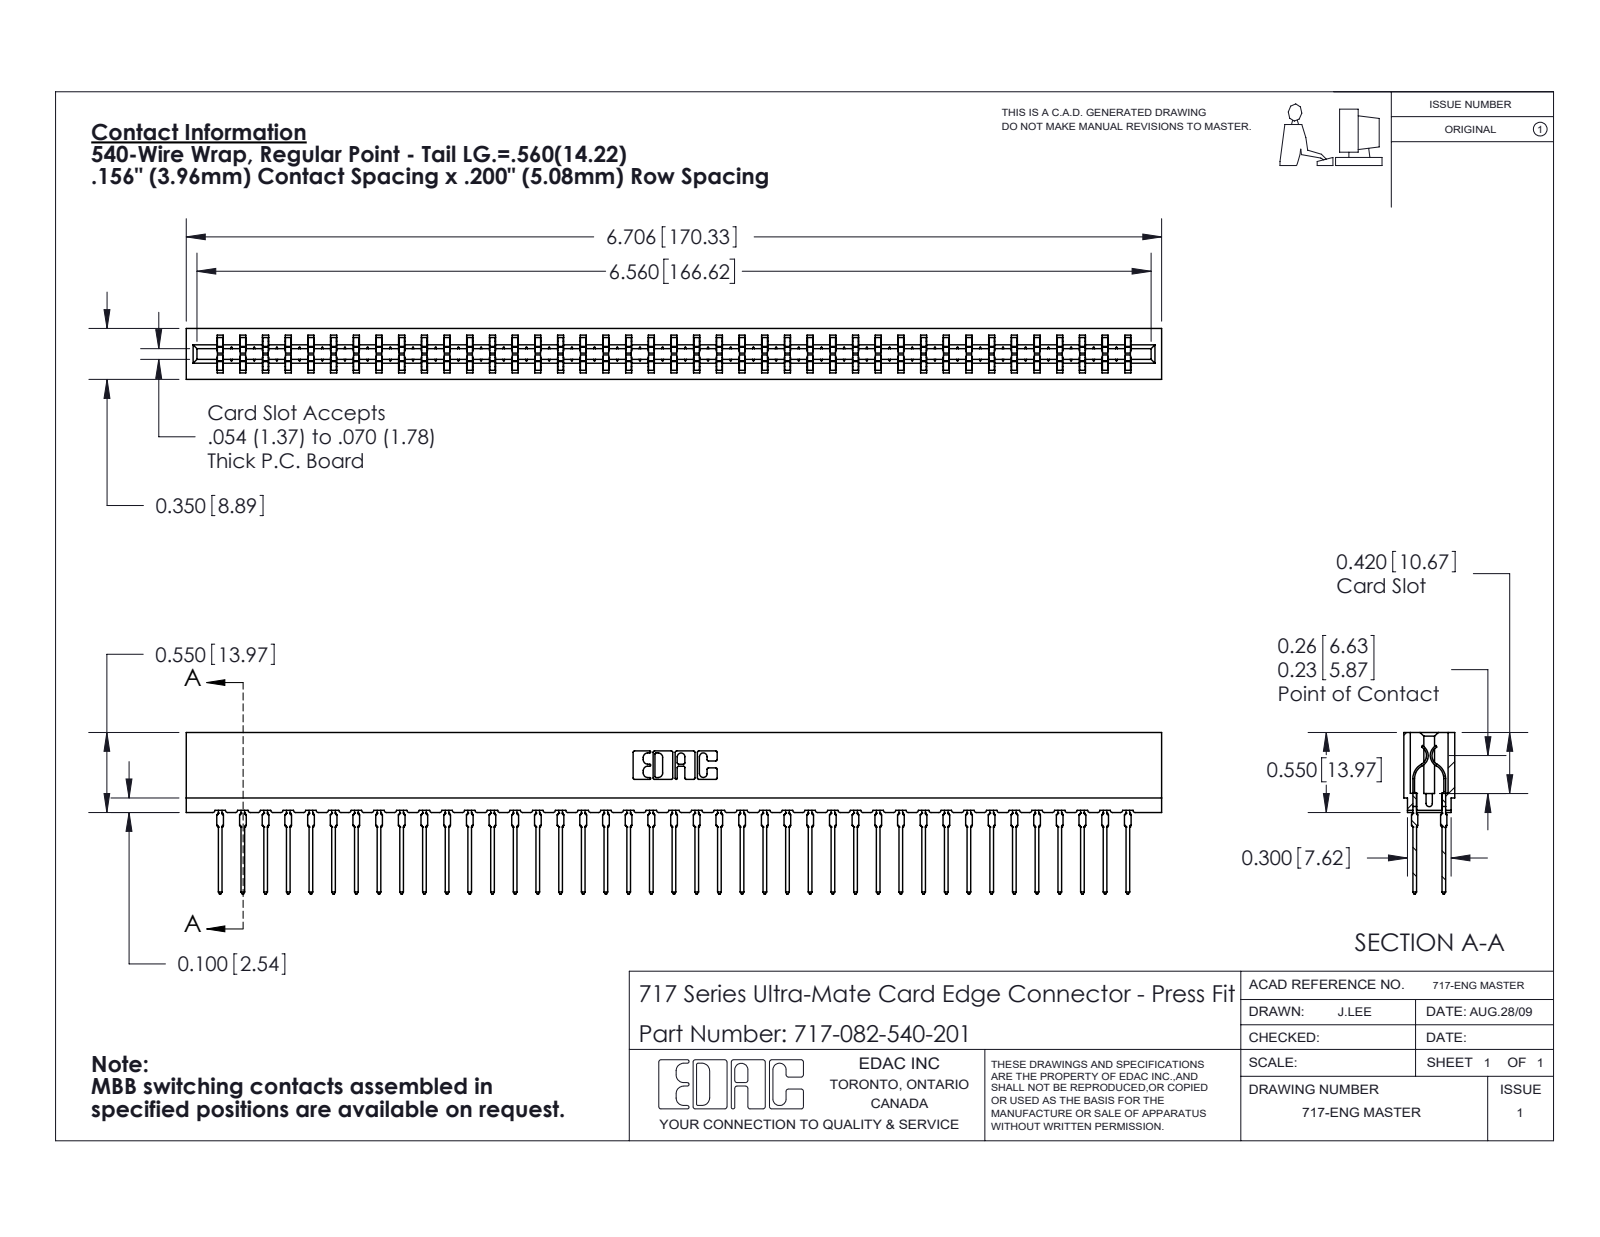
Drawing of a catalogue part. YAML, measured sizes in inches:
part_name: "745-292-001_540; 717-082-540-201; 717 Part_Insulator Option - 06"
step_written_by: "SolidWorks 2020 (CONFIG_CONTROL_DESIGN)"
units: inches
bodies: {solids: 83, faces: 7474, planar: 3867, cylindrical: 1475, other: 2132}
overall_size: [6.706, 1.109, 0.35]
volume: 0.916
surface_area: 37.21
partial_cylinders:
  - {radius: 0.021, count: 164}
  - {radius: 0.015, count: 82}
  - {radius: 0.01, count: 22}
  - {radius: 0.005, count: 8}
  - {radius: 0.011, count: 8}
  - {radius: 0.007, count: 6}
  - {radius: 0.031, count: 6}
  - {radius: 0.026, count: 3}
face_to_face_distances: [0.212, 0.138, 0.35, 0.063, 0.287, 0.076, 0.149, 0.074, 0.087, 0.263]
